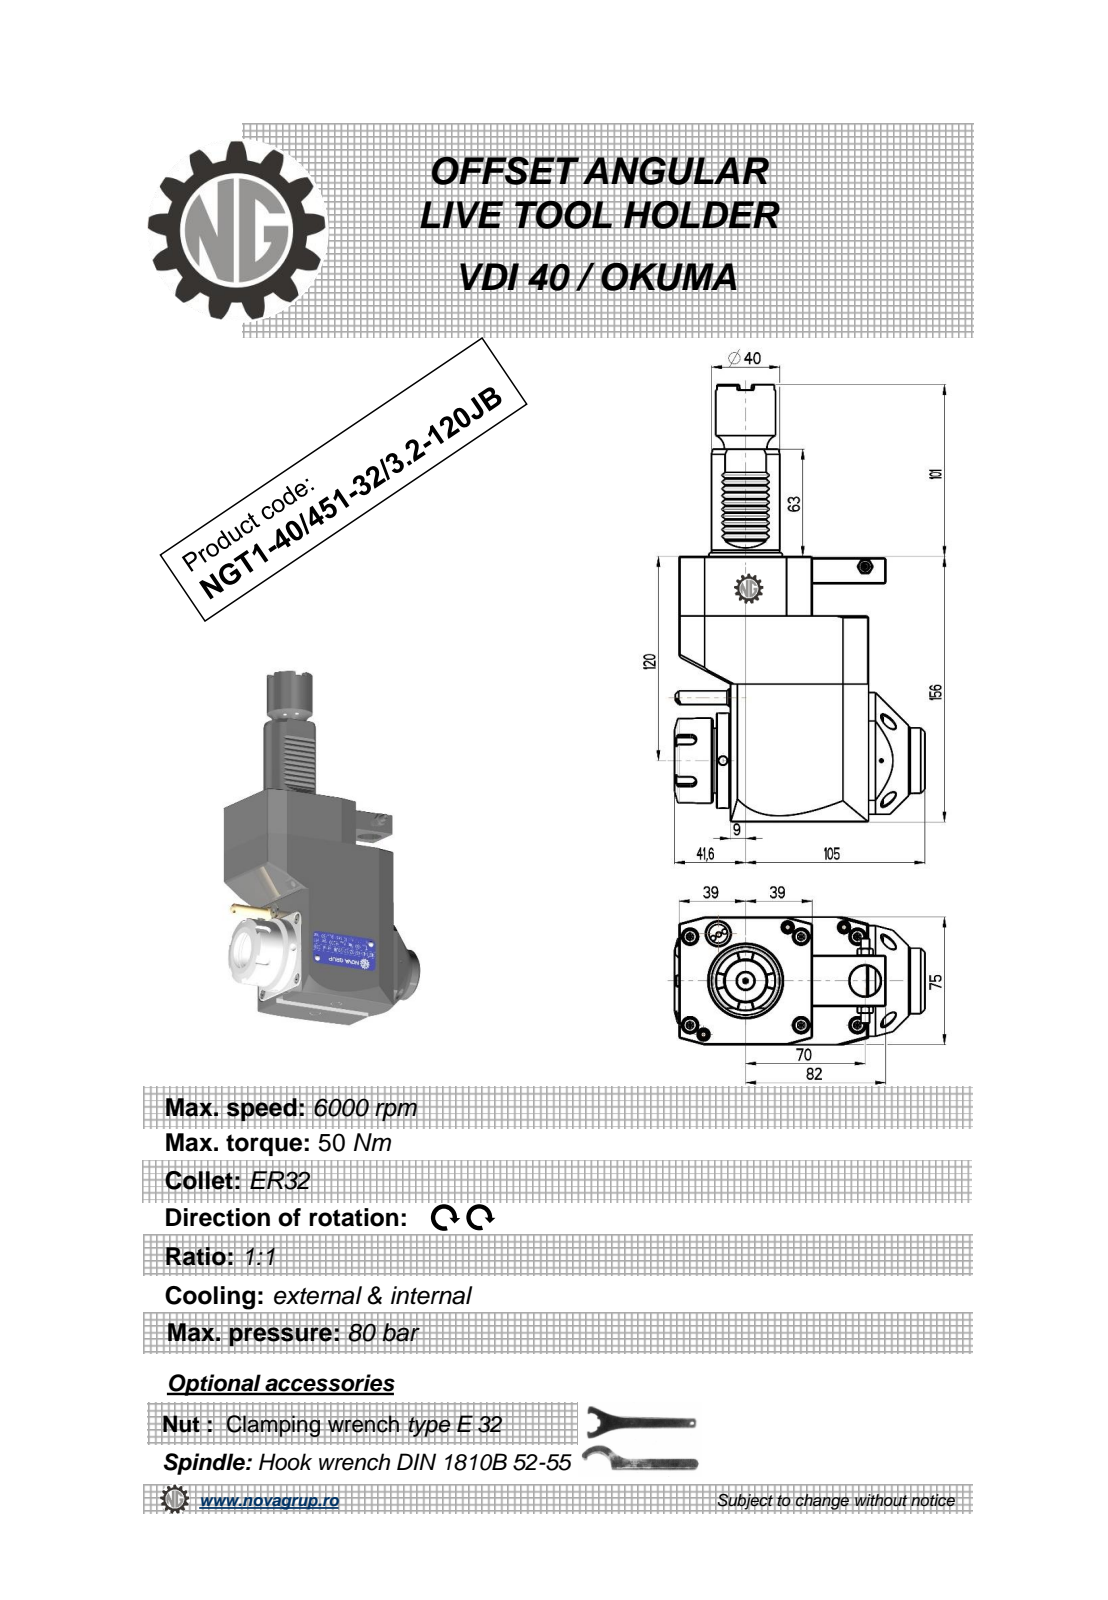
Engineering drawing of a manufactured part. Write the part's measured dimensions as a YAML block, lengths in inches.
part_name: "NGT1_40_451_32_3_2_120JB"
step_written_by: "PRO/ENGINEER BY PARAMETRIC TECHNOLOGY CORPORATION, 2010280 (CONFIG_CONTROL_DESIGN)"
units: inches
bodies: {solids: 1, faces: 480, planar: 217, cylindrical: 89, other: 174}
overall_size: [10.118, 5.772, 2.953]
volume: 76.77
surface_area: 149.4
round_holes:
  - {diameter: 0.197, count: 3}
  - {diameter: 0.118, count: 1}
  - {diameter: 0.165, count: 1}
  - {diameter: 0.374, count: 1}
  - {diameter: 0.709, count: 1}
  - {diameter: 0.984, count: 1}
  - {diameter: 1.063, count: 1}
round_bosses_or_shafts:
  - {diameter: 2.205, count: 1}
  - {diameter: 1.969, count: 1}
  - {diameter: 1.693, count: 1}
  - {diameter: 1.575, count: 1}
  - {diameter: 1.516, count: 1}
  - {diameter: 1.378, count: 1}
  - {diameter: 0.394, count: 1}
  - {diameter: 0.353, count: 1}
partial_cylinders:
  - {radius: 0.01, count: 12}
  - {radius: 0.012, count: 10}
  - {radius: 0.008, count: 6}
  - {radius: 0.118, count: 5}
  - {radius: 0.02, count: 1}
  - {radius: 1.575, count: 1}
face_to_face_distances: [2.953, 6.142, 4.37, 1.299, 4.764, 1.181, 1.378, 3.189, 3.678, 3.071]
hole_center_spacings: [0.522, 1.611, 2.756, 3.051, 3.278, 4.429, 5.557]
